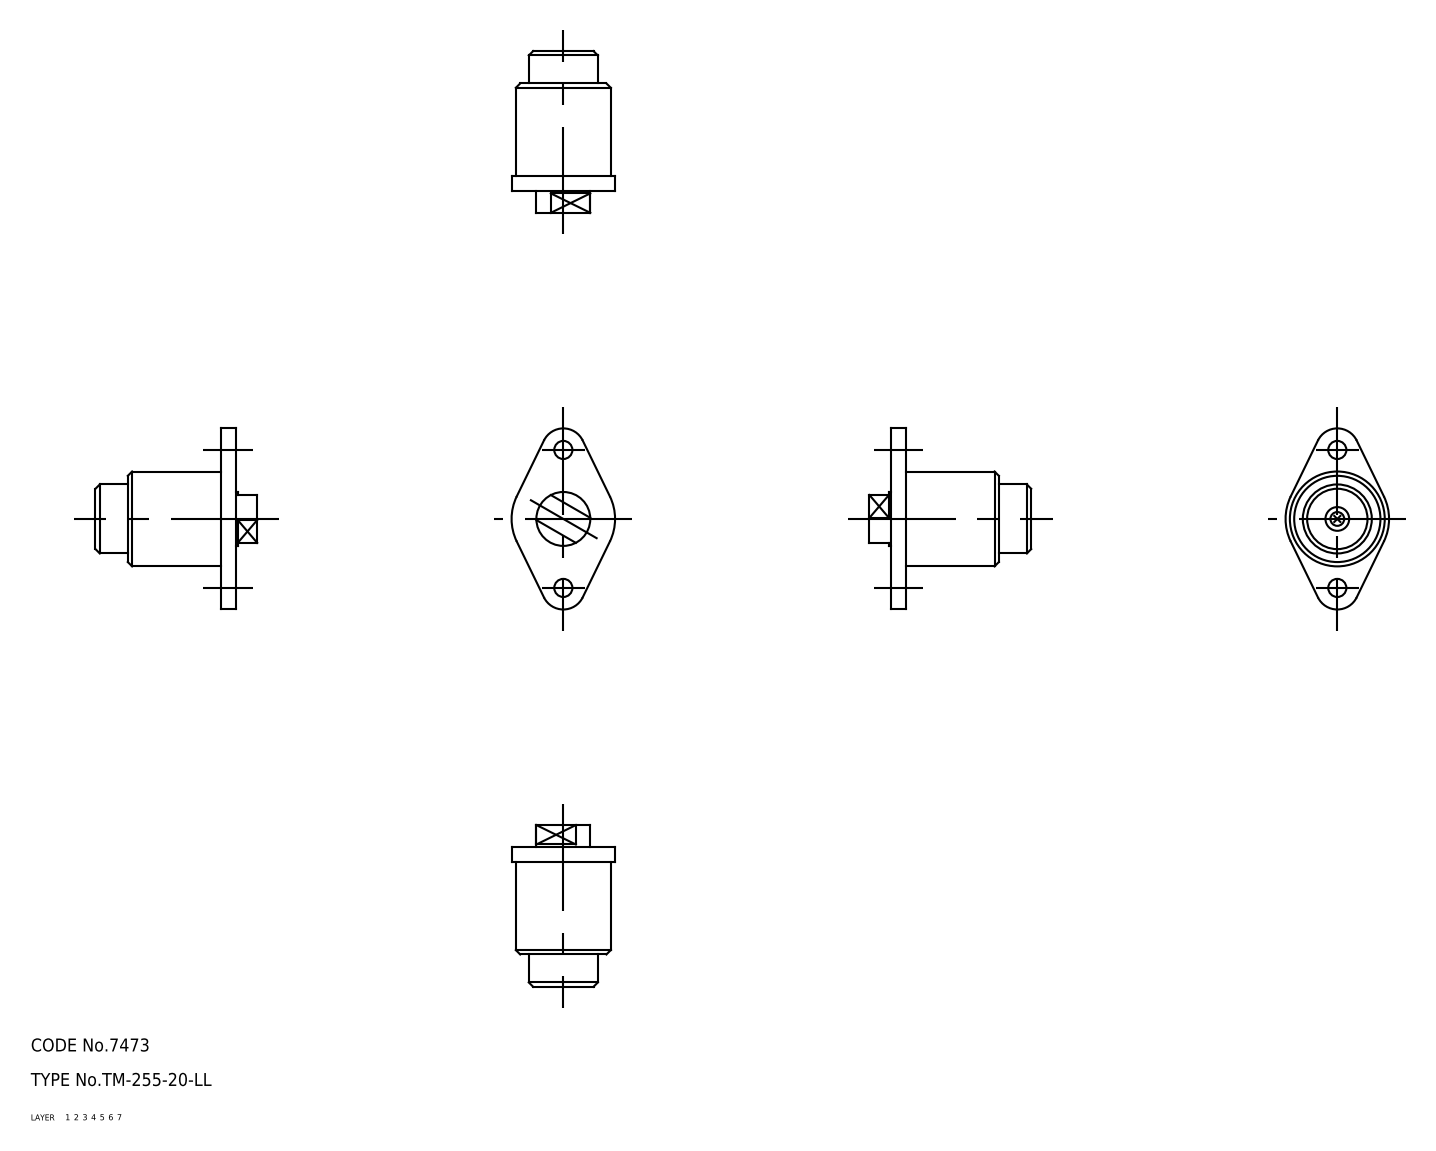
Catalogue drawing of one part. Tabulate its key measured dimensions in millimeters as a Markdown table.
| quantity | value |
| --- | --- |
| part name | shaft; housing; TM_255_20_LL_15_36 |
| STEP written by | CADfix (AUTOMOTIVE_DESIGN) |
| units | millimeters |
| bodies | 2 solids, 56 faces (0 planar, 0 cylindrical, 56 other) |
| overall size | 42 × 37.5 × 24 |
| volume | 12 288 mm³ |
| surface area | 4 263 mm² |
